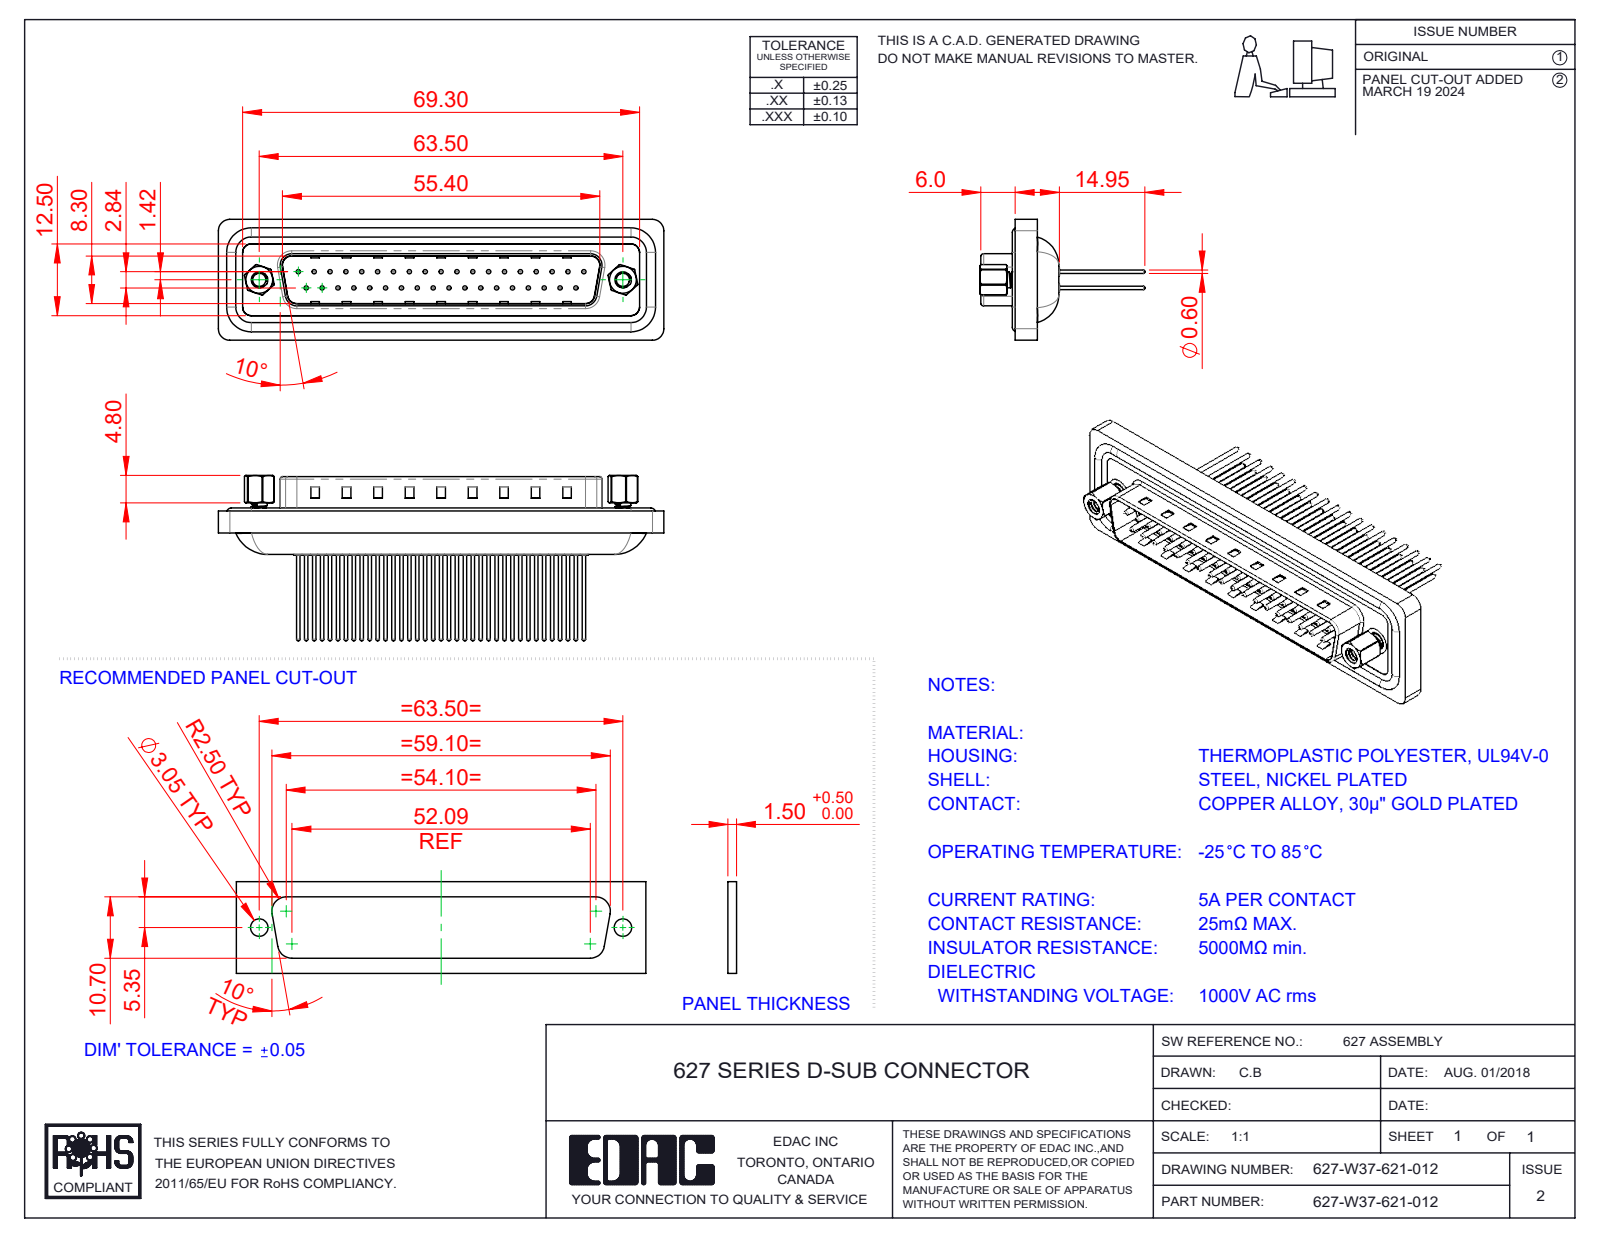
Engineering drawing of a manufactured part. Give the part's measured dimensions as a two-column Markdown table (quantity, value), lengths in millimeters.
| quantity | value |
| --- | --- |
| part name | 627-W37-621-012; 627W Contact Row 1_21; 627W Waterproof Housing_37 Contacts; 627W Contact Row 2_21 (+4 more) |
| STEP written by | SolidWorks 2023 (CONFIG_CONTROL_DESIGN) |
| units | millimeters |
| bodies | 45 solids, 1999 faces (496 planar, 816 cylindrical, 687 other) |
| overall size | 77.8 × 28.85 × 21.1 |
| volume | 9 678 mm³ |
| surface area | 15 182 mm² |
| round holes (diameter × count) | 0.75 × 37, 1.5 × 37, 1.6 × 37, 2 × 37, 2.26 × 2, 2.29 × 2, 4 × 2, 4.8 × 2, 5 × 2 |
| round bosses / shafts (diameter × count) | 0.6 × 37, 1.5 × 9, 1.6 × 4, 4.9 × 2, 2.79 × 2 |
| partial cylindrical surfaces (radius × count) | 2 × 16, 1.5 × 14, 0.5 × 8, 2.7 × 6, 0.9 × 4, 1.6 × 4, 4.3 × 4, 0.4 × 2 |
| main face-to-face distances | 0.75, 0.4, 4.1, 1.1, 2.75, 4.6, 3.75, 5.65, 15.45, 14.7 |
| hole center spacings | 3.16, 2.77, 5.54, 8.31, 5.04, 10.1, 11.08, 12.78 |
